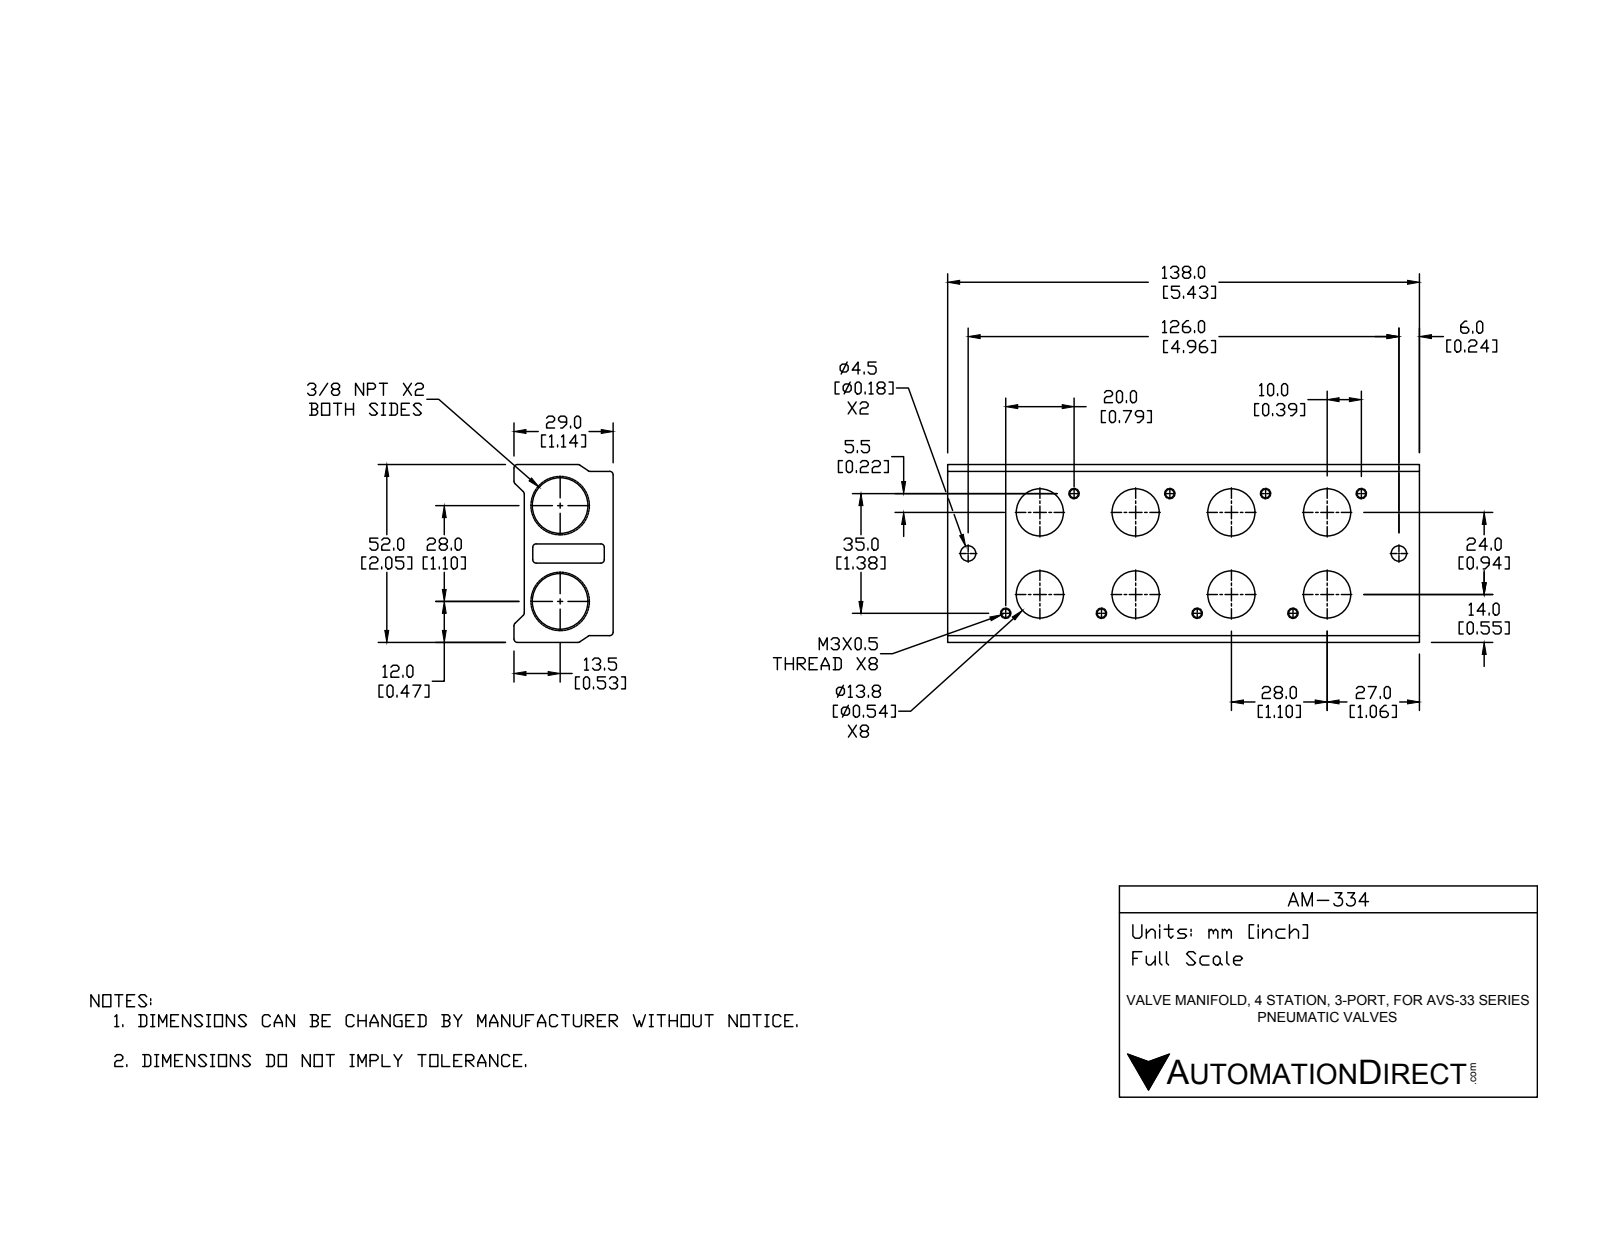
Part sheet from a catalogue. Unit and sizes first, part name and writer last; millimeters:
Units: millimetres
Overall size (bounding box): 138 × 52 × 29
Round holes (diameter × count): ⌀2.5 ×8, ⌀13.8 ×8, ⌀4.5 ×2, ⌀11.11 ×2, ⌀14.27 ×2
Partial cylindrical surfaces — rounded edges, fillets, slot ends (radius × count): R1 ×16
Main face-to-face distances: 23.2, 28.8, 26, 5.6, 52, 2, 50, 21.2, 26.8, 3
Hole centre spacings: 28, 11.41, 31.15, 56, 18.82, 34.56, 36.88, 38.4
Volume: 122 122 mm³ · Surface area: 44 171 mm²
Bodies: 1 solid, 154 faces (26 planar, 76 cylindrical, 52 other)
Part name (STEP PRODUCT): AM-334
STEP written by: SolidWorks 2016 (AUTOMOTIVE_DESIGN)
